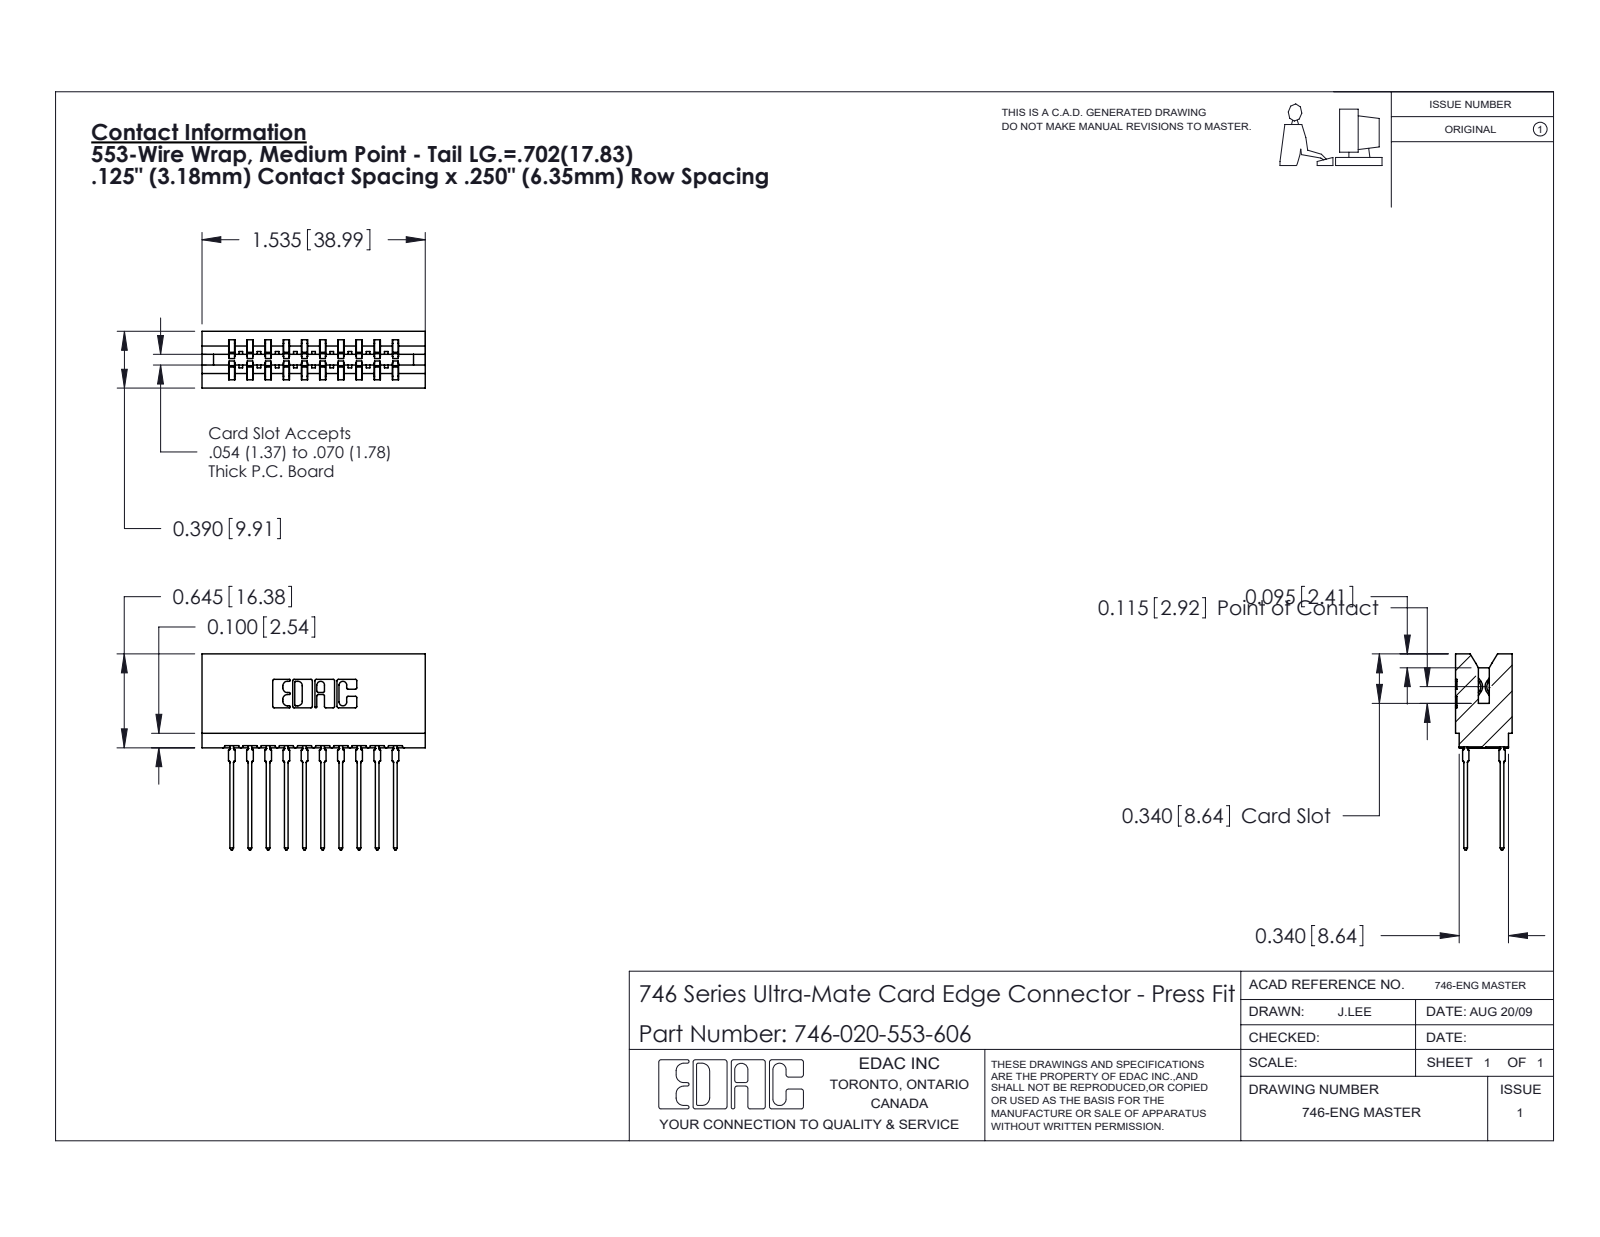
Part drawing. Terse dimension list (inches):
name: 746 Part_.340 Slot Depth - 06; 746-292-001_553; 746-020-553-606
written by: SolidWorks 2020 (CONFIG_CONTROL_DESIGN)
unit: in
bodies: 21 solids, 1888 faces (976 planar, 392 cylindrical, 520 other)
size: 1.535 × 1.346 × 0.39
volume: 0.289 in³; area: 10.52 in²
rounds: 40× R0.021, 22× R0.01, 11× R0.015, 8× R0.005, 8× R0.011, 6× R0.007, 6× R0.031, 3× R0.026
face distances: 0.25, 0.057, 0.333, 0.5, 0.042, 0.125, 0.083, 0.75, 0.125, 0.025
